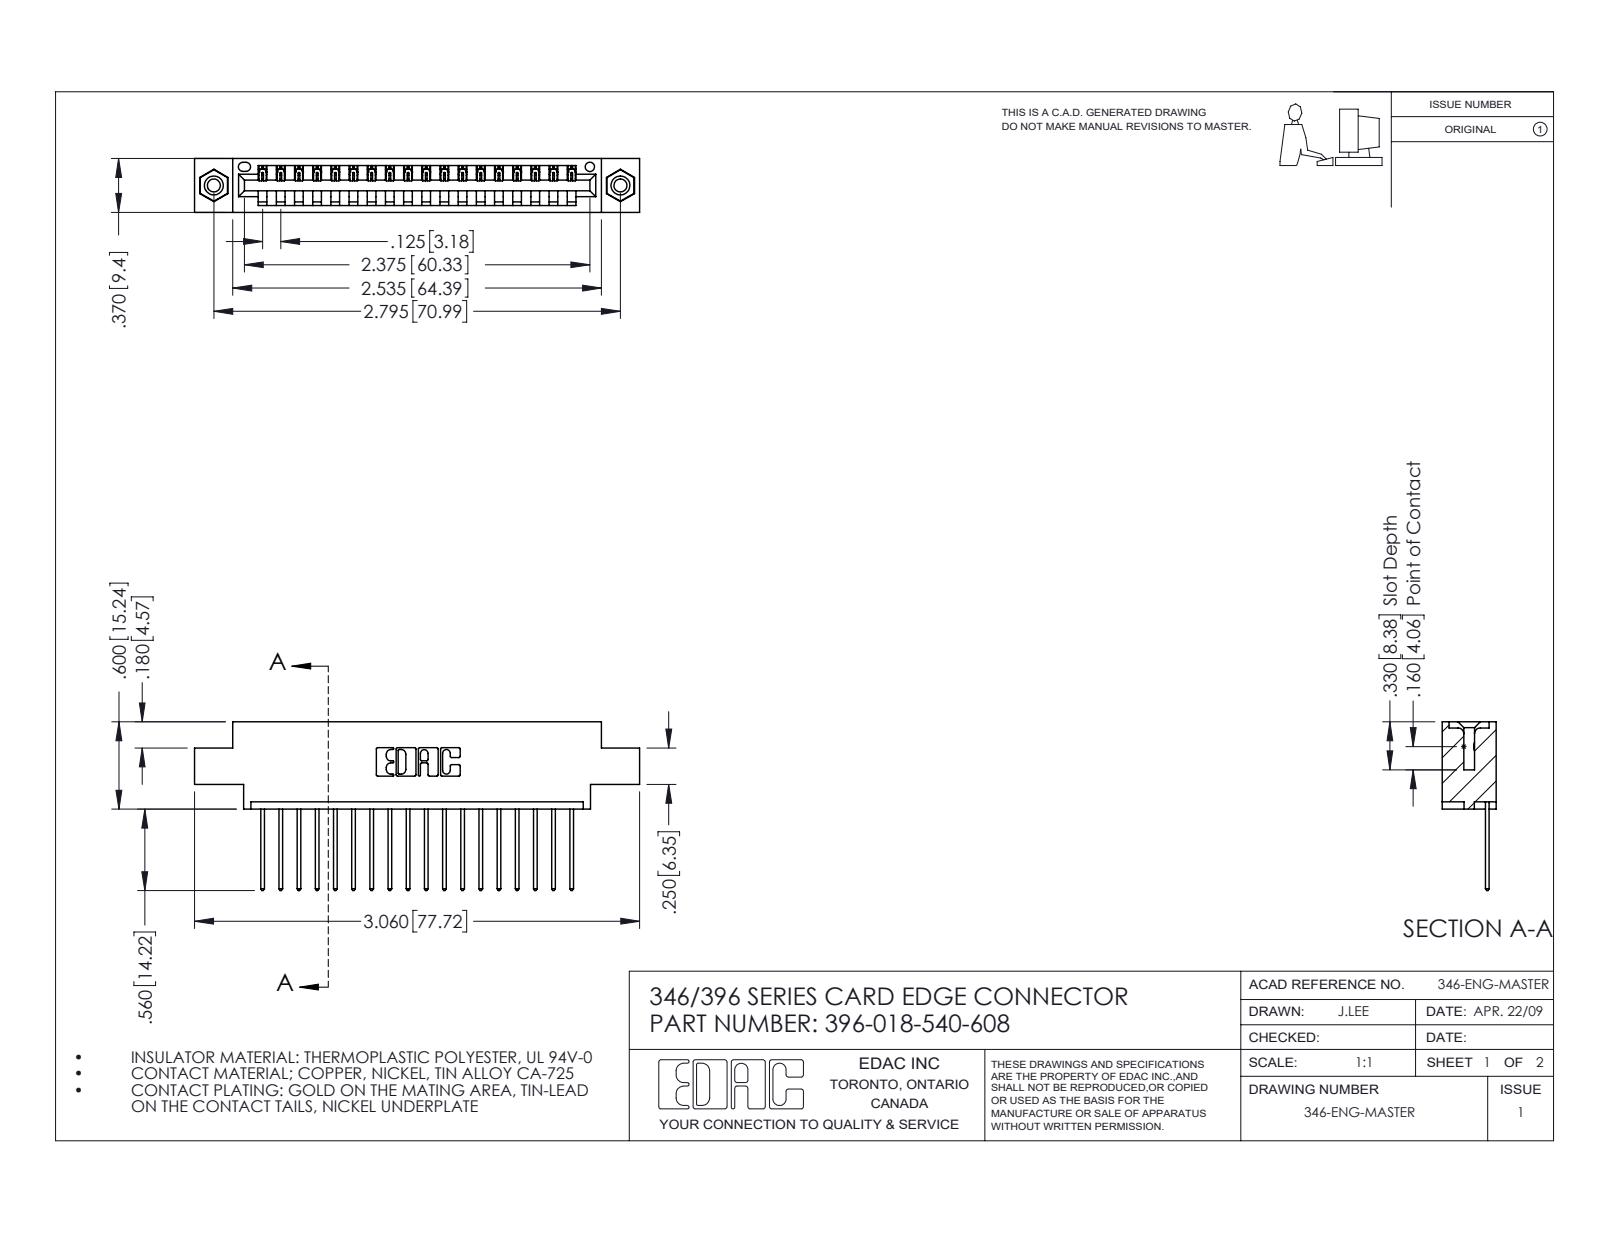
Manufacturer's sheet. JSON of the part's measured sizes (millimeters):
{"part_name": "345-250-001_345-250-003-102; 346 Part_0.170 Offset - 0.156 Dia-TI; 396-018-540-608; 345-292-001_345-293-140", "step_written_by": "SolidWorks 2016 (CONFIG_CONTROL_DESIGN)", "units": "millimeters", "bodies": {"solids": 21, "faces": 1230, "planar": 832, "cylindrical": 382, "other": 16}, "overall_size": [77.7, 29.5, 9.4], "volume_mm3": 7140, "surface_area_mm2": 9019, "round_holes": [[2.3, 2], [3.2, 2], [4, 2], [1.6, 1]], "round_bosses_or_shafts": [[3.9, 2]], "partial_cylinders_radius": [[0.2, 36], [0.3, 36], [0.3, 22], [0.2, 6], [0.8, 6], [0.7, 3], [0.8, 2], [1, 2]], "face_to_face_distances": [1.2, 8.2, 9.4, 6.4, 1.8, 7.6, 0.6, 5.6, 3.8, 2.5], "hole_center_spacings": [6.2, 65.7, 71]}
